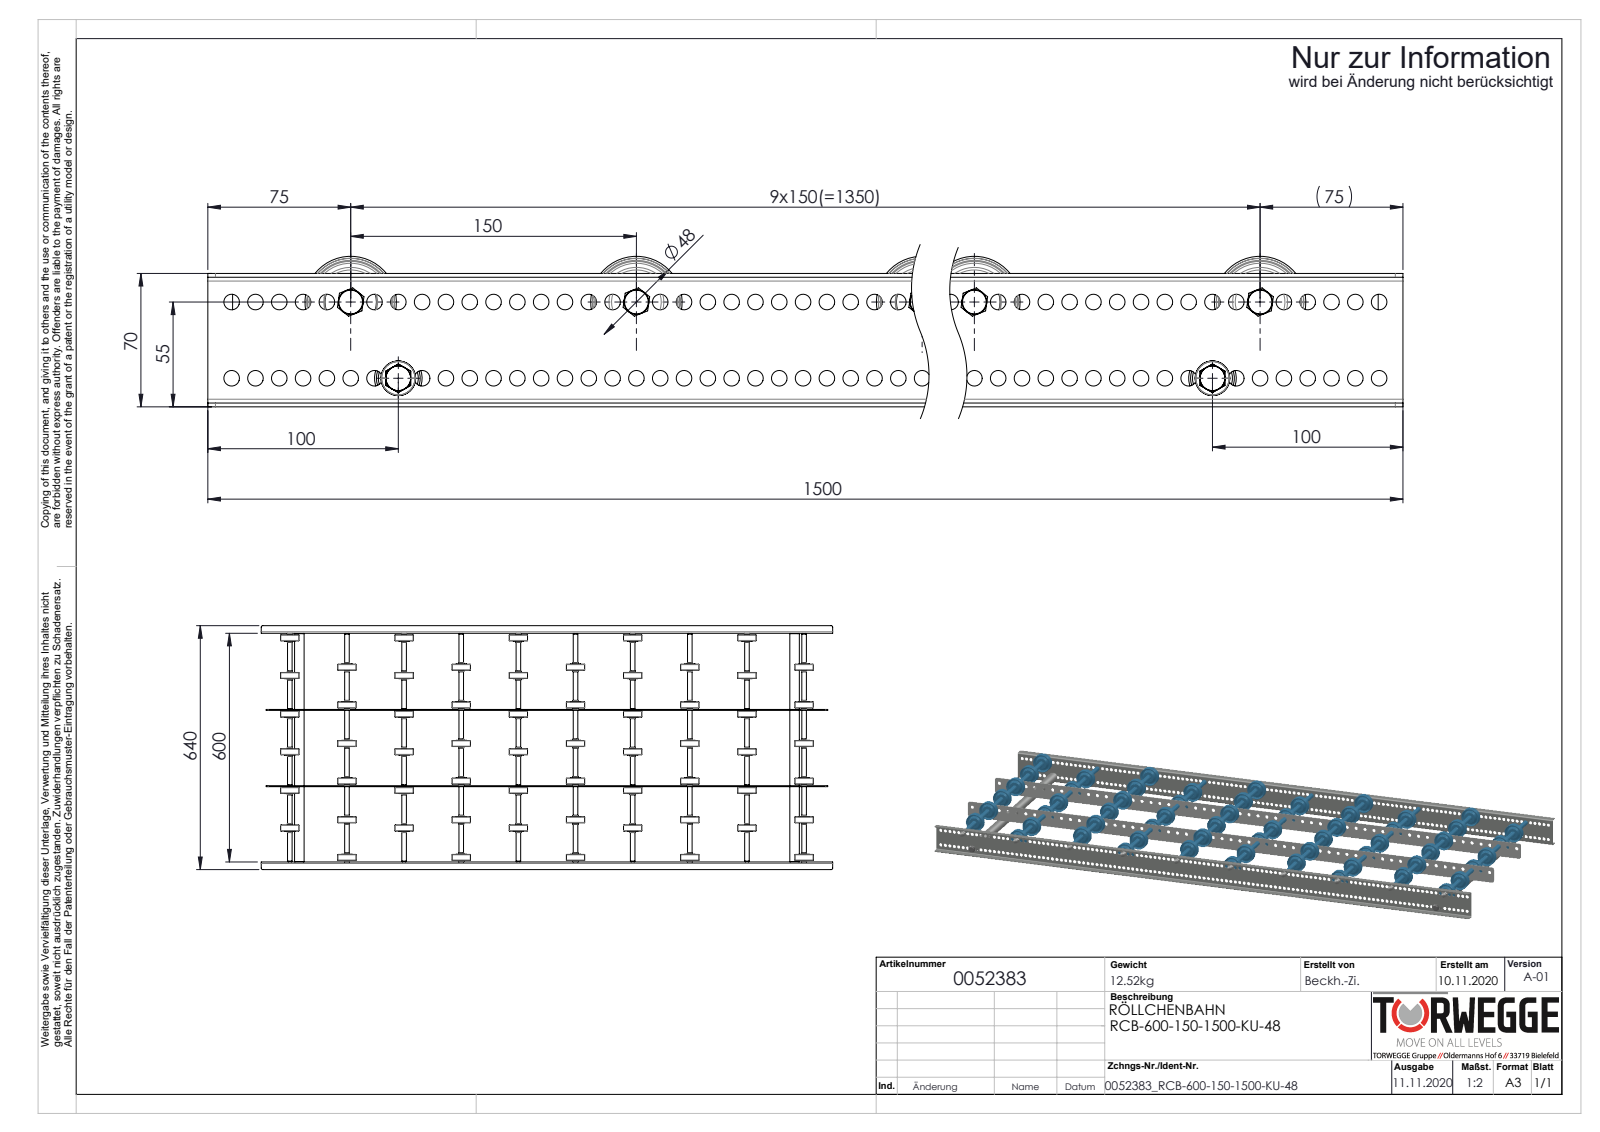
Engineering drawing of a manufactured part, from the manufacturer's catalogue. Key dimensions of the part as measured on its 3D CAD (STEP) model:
Part name (STEP PRODUCT): S106837_Gewindestange-M8-KFG_L620; S100100_Längstraverse-42x2,5_S100102_Lngstraverse-RB-L1500; Hutmutter_DIN_1587_M8; Profil_LRB-20x70x20x2_KFG_S100201_U-PROFIL-20-70-20-2-LRB-L=1500 (+6 more)
STEP written by: SolidWorks 2020 (AUTOMOTIVE_DESIGN)
Units: millimetres
Bodies: 164 solids, 6628 faces (1092 planar, 2672 cylindrical, 2864 other)
Overall size (bounding box): 1500 × 640 × 79
Volume: 2 715 000 mm³ · Surface area: 2 111 000 mm²
Round holes (diameter × count): ⌀8.2 ×238, ⌀8.5 ×59, ⌀6.65 ×10, ⌀9.65 ×10, ⌀13.7 ×10, ⌀6.8 ×2, ⌀21 ×2
Round bosses / shafts (diameter × count): ⌀8 ×12, ⌀48 ×10, ⌀27 ×10, ⌀12.7 ×10, ⌀12.5 ×10, ⌀12 ×10, ⌀25 ×2
Partial cylindrical surfaces — rounded edges, fillets, slot ends (radius × count): R4 ×8, R2 ×4, R5 ×4
Main face-to-face distances: 2, 200.1, 602, 2.5, 197.6, 68, 604, 600, 400.2, 201.8
Hole centre spacings: 12.5, 25, 37.5, 50, 62.5, 75, 87.5, 100
